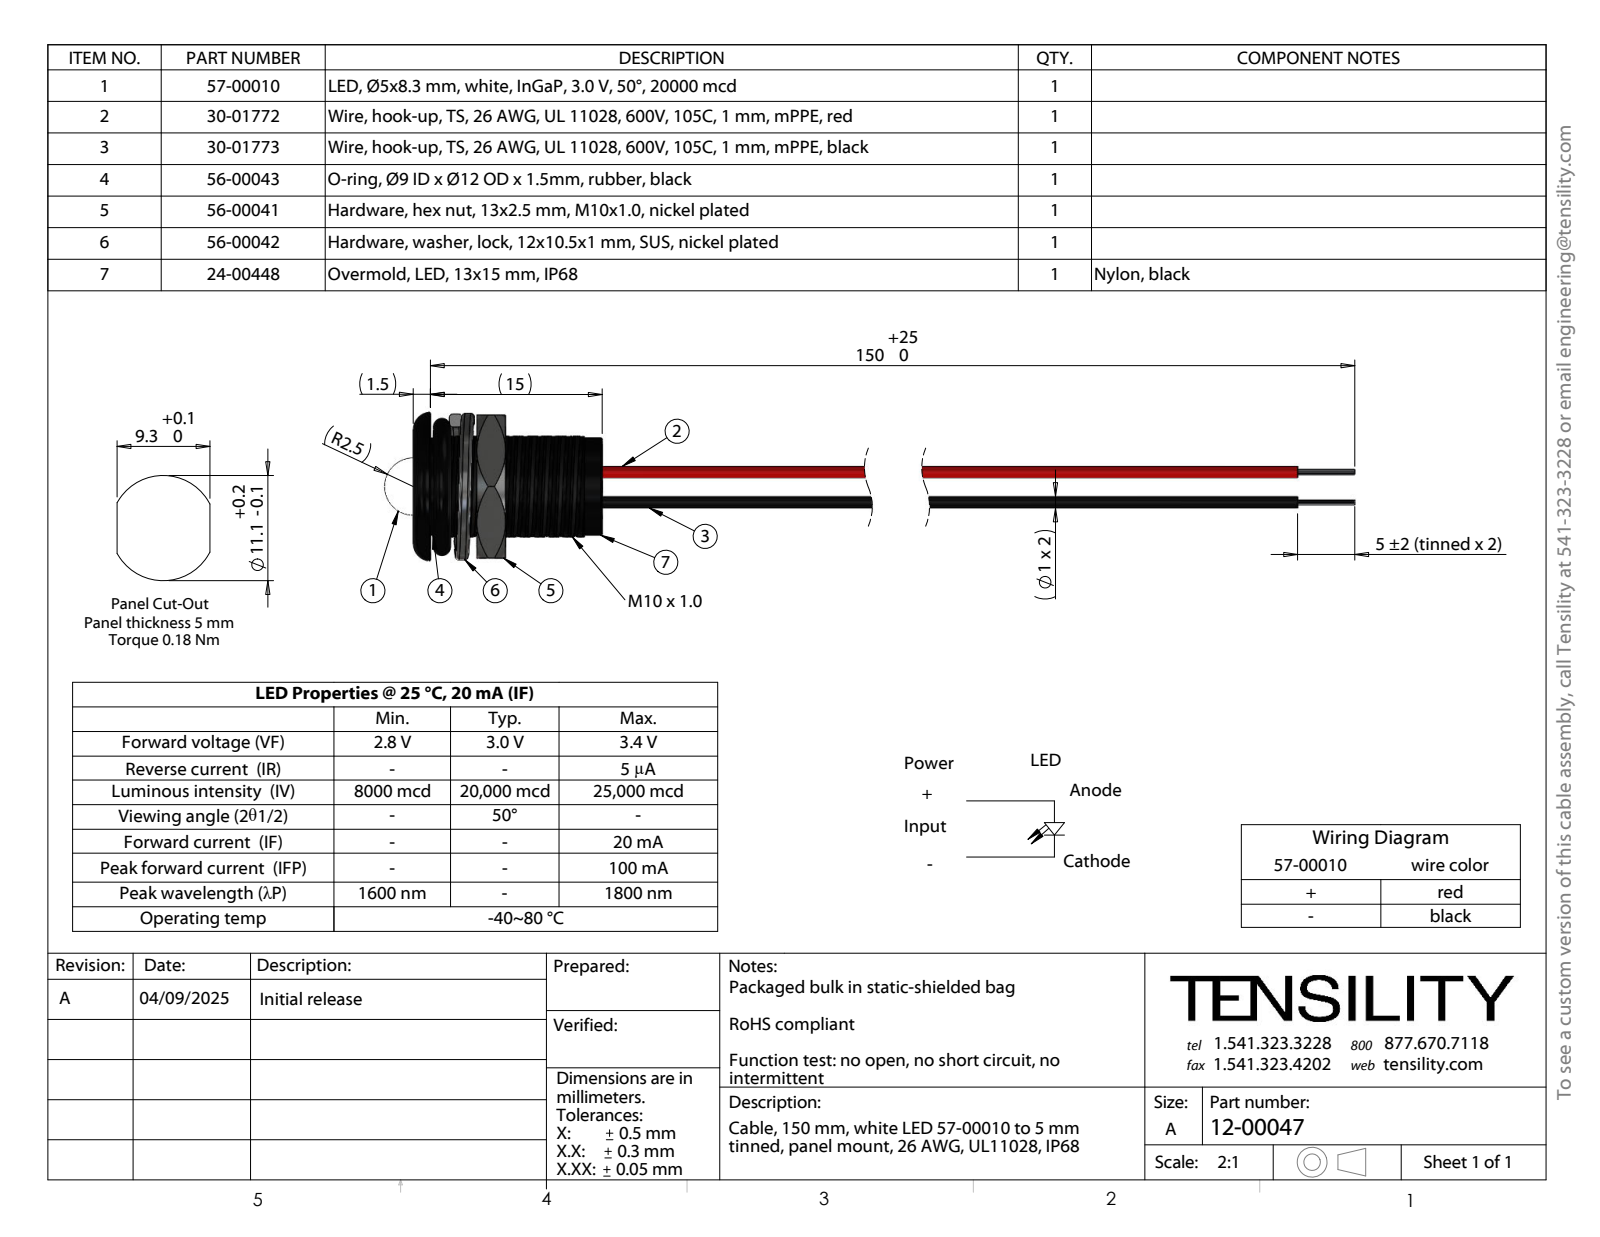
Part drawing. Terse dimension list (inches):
name: 56-00041; 57-00010_trimmed leads; 24-00448; 30-01772_stripped and tinned (+4 more)
written by: SolidWorks 2021 (CONFIG_CONTROL_DESIGN)
unit: in
bodies: 57 solids, 514 faces (185 planar, 246 cylindrical, 83 other)
size: 6.85 × 0.568 × 0.511
volume: 0.108 in³; area: 10.18 in²
holes: 2× ⌀0.039
bosses: 2× ⌀0.039, 2× ⌀0.033, 1× ⌀0.335, 1× ⌀0.197
rounds: 1× R0.17, 1× R0.197
face distances: 0.059, 0.65, 0.591, 0.492, 0.317, 0.258, 0.332, 0.219, 0.16, 0.098
hole spacings: 0.014, 0.015, 0.013, 0.096, 0.093, 0.098, 0.099, 0.101
